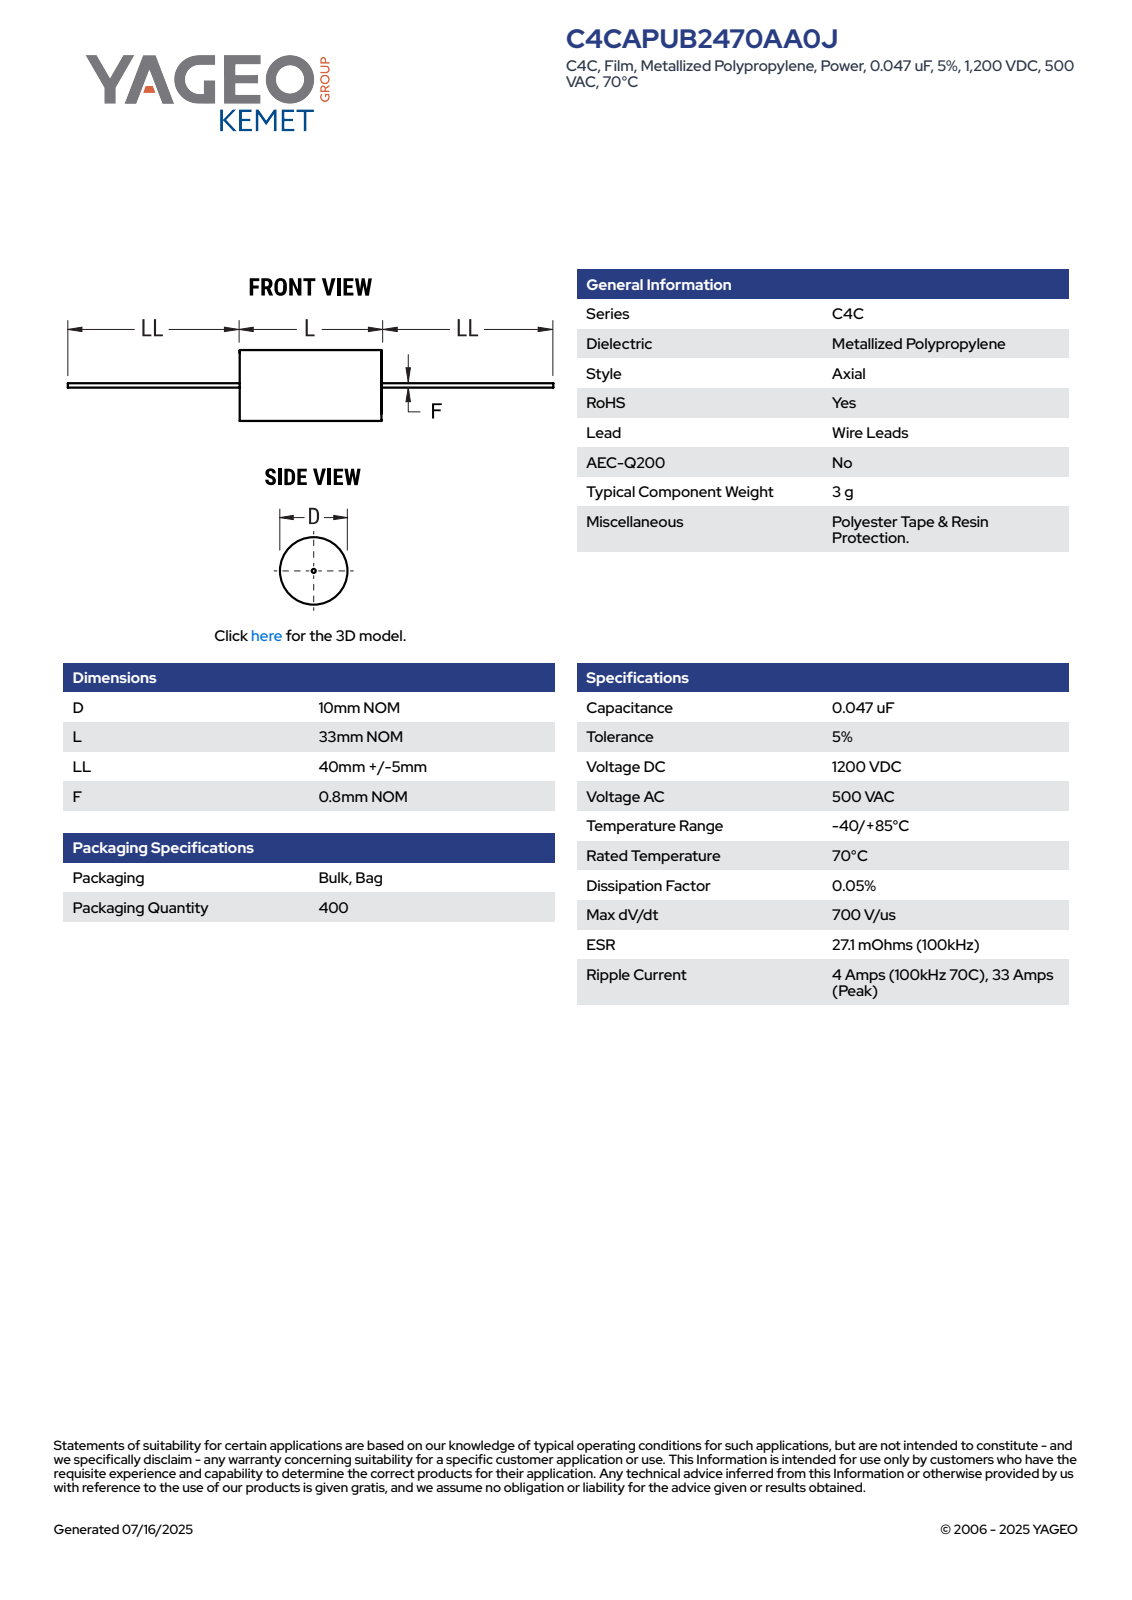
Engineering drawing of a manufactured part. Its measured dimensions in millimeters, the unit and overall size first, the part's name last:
Units: millimetres
Overall size (bounding box): 123 × 10 × 10
Round bosses / shafts (diameter × count): ⌀10 ×1, ⌀0.8 ×1
Partial cylindrical surfaces — rounded edges, fillets, slot ends (radius × count): R4.99 ×1
Main face-to-face distances: 33.01, 33, 45, 78, 44.99, 123, 78.01
Volume: 2 637 mm³ · Surface area: 1 577 mm²
Bodies: 2 solids, 87 faces (28 planar, 28 cylindrical, 31 other)
Part name (STEP PRODUCT): CFP_ACWF_10X33_D10L33LL45F0.8
STEP written by: SolidWorks 2014 (AUTOMOTIVE_DESIGN)
